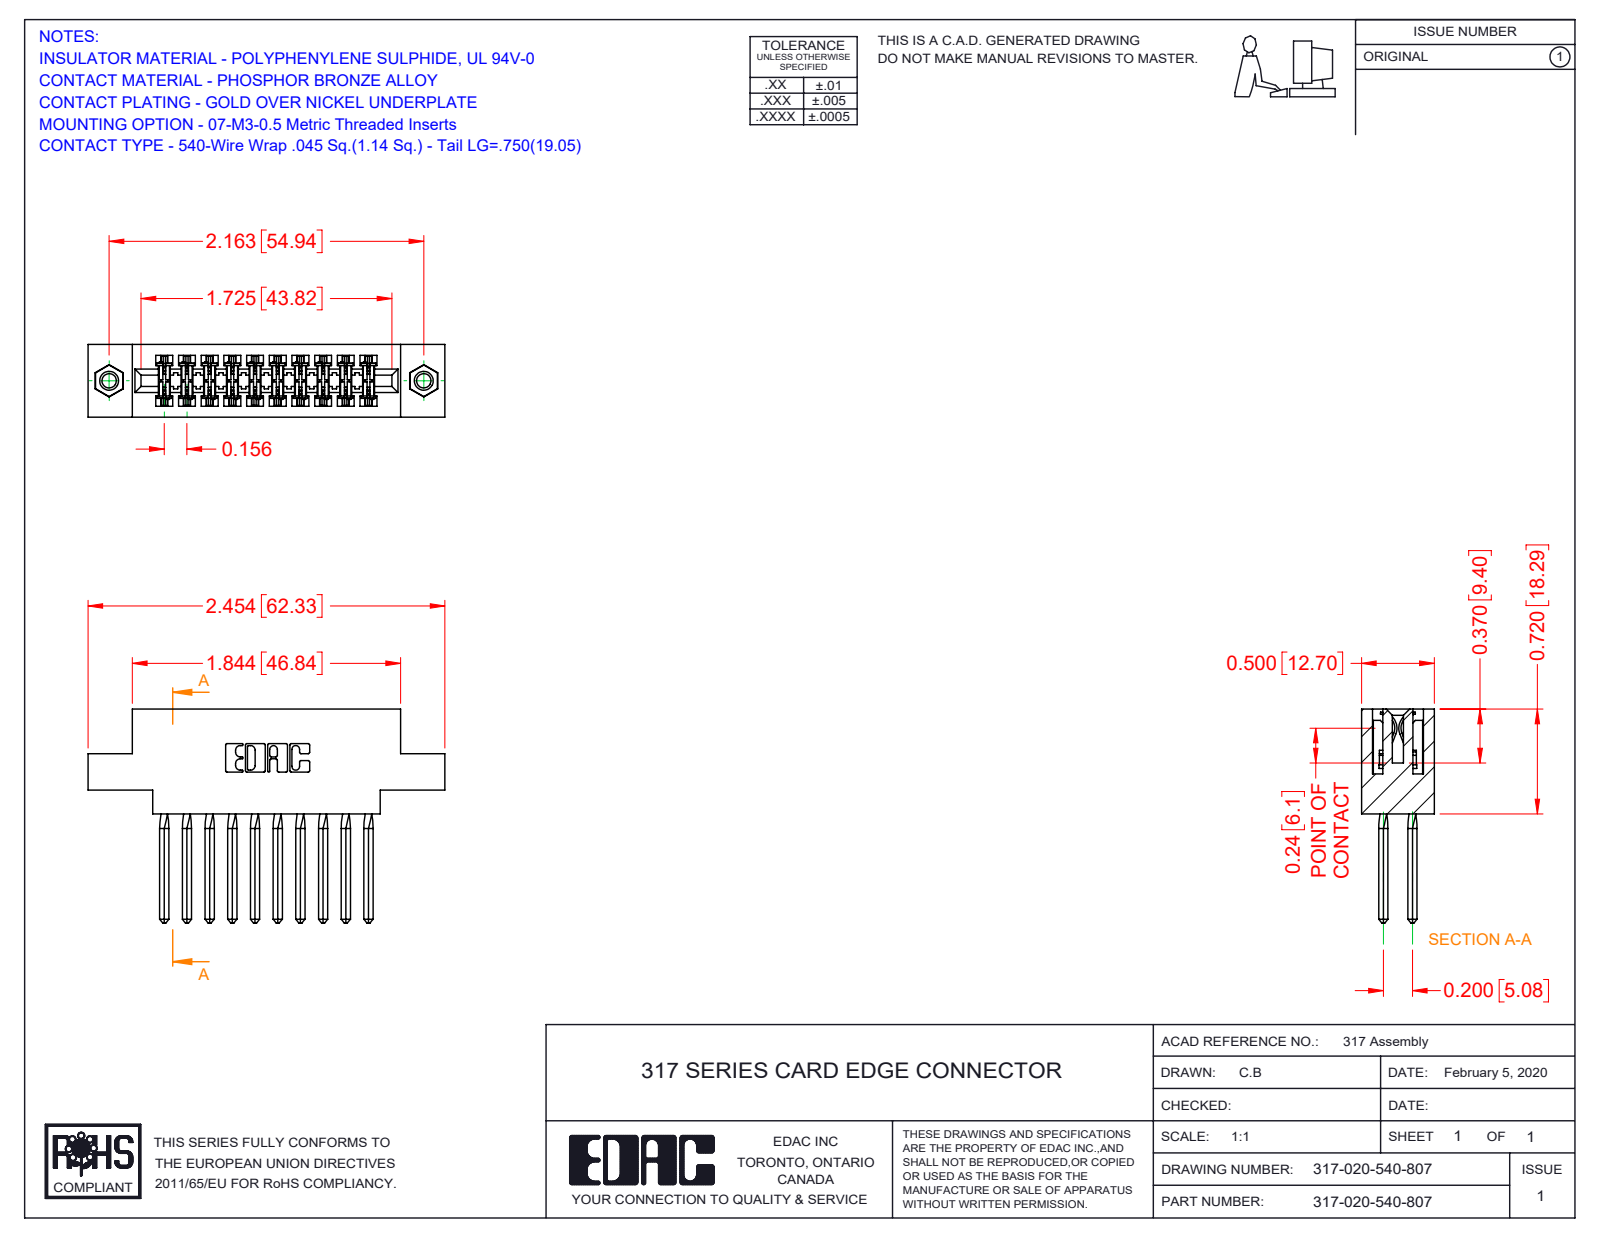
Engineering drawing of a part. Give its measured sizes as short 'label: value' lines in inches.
name: 317-020-540-807; 345-250-001_345-250-005-103; 317-290-001_540; 317 Part_.156 Dia - TI
written by: SolidWorks 2016 (CONFIG_CONTROL_DESIGN)
unit: in
bodies: 23 solids, 1942 faces (1550 planar, 296 cylindrical, 96 other)
size: 2.454 × 1.47 × 0.5
volume: 0.572 in³; area: 19.83 in²
holes: 2× ⌀0.098, 2× ⌀0.125, 2× ⌀0.156
bosses: 2× ⌀0.155
rounds: 40× R0.015, 22× R0.01, 6× R0.007, 6× R0.031, 3× R0.026, 2× R0.095, 2× R0.1, 2× R0.11
face distances: 0.5, 0.075, 0.425, 0.11, 0.22, 0.35, 0.331, 0.156, 0.116, 0.305
hole spacings: 2.163
